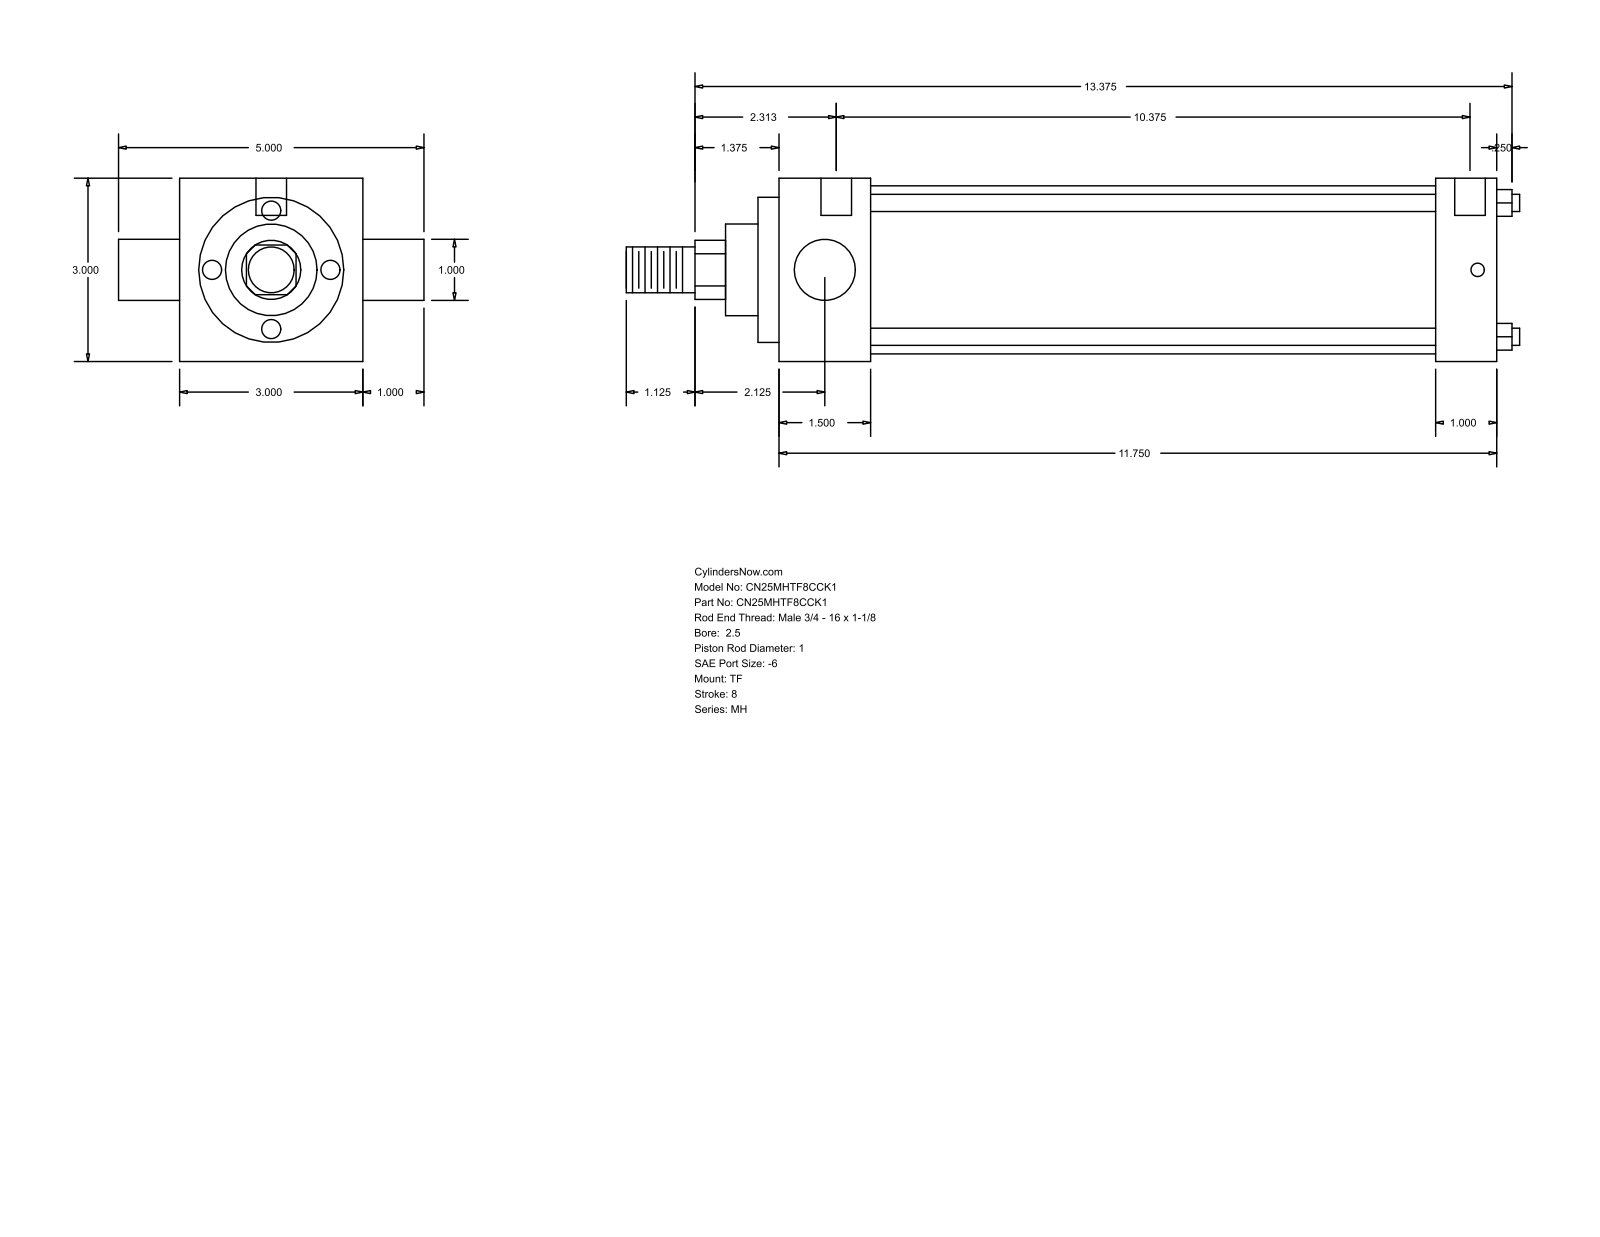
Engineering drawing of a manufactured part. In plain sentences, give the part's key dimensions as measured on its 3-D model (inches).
The part is named "MH_TF__0250_1". Its 3-D file was written by "GSSL Pune (CONFIG_CONTROL_DESIGN)". It is 0 solids with 86 faces: 61 planar, 25 cylindrical and 0 other. Overall it measures 14.625 by 5 by 3 inches. Round holes: 3 of diameter 0.219, 2 of diameter 0.5. Round bosses or shafts: 4 of diameter 0.281, 2 of diameter 1, 1 of diameter 2.75, 1 of diameter 2.375, 1 of diameter 1.5, 1 of diameter 0.75. Partial cylindrical surfaces (rounded edges, fillets, slot ends): 1 of radius 0.484. The main face-to-face distances are 3, 11.75, 1, 1.5, 10.25, 10.75, 9.25, 0.344, 1.844, 11.094. The hole center spacings are 0.125, 0.187, 10.375, 10.5, 10.562, 10.687.
